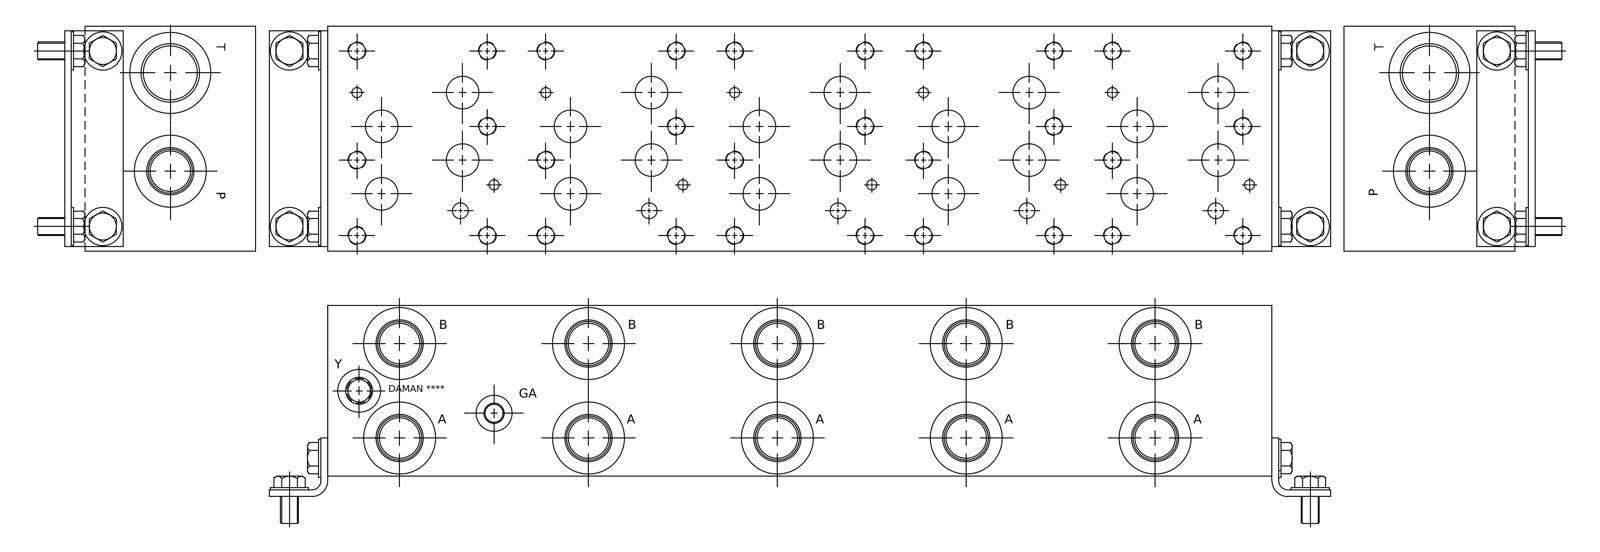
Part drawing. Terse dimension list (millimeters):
name: Part_AD08P055S_3D
written by: Autodesk Inventor 2019 (AUTOMOTIVE_DESIGN)
unit: mm
bodies: 1 solid, 1028 faces (473 planar, 193 cylindrical, 362 other)
size: 666.75 × 158.75 × 120.65
volume: 12 070 000 mm³; area: 528 400 mm²
holes: 33× ⌀10.72, 32× ⌀12.7, 19× ⌀23.01, 11× ⌀31.27, 11× ⌀33.76, 11× ⌀49.12, 10× ⌀7.14, 10× ⌀28.57, 10× ⌀33.35, 10× ⌀35.51, 4× ⌀11.13, 2× ⌀33.34
face distances: 120.65, 158.75, 666.75, 0.79, 157.96, 665.96, 665.17, 19.84, 19.05, 90.42
hole spacings: 133.35, 266.7, 400.05, 191.98, 270.92, 61.92, 210.9, 79.84
